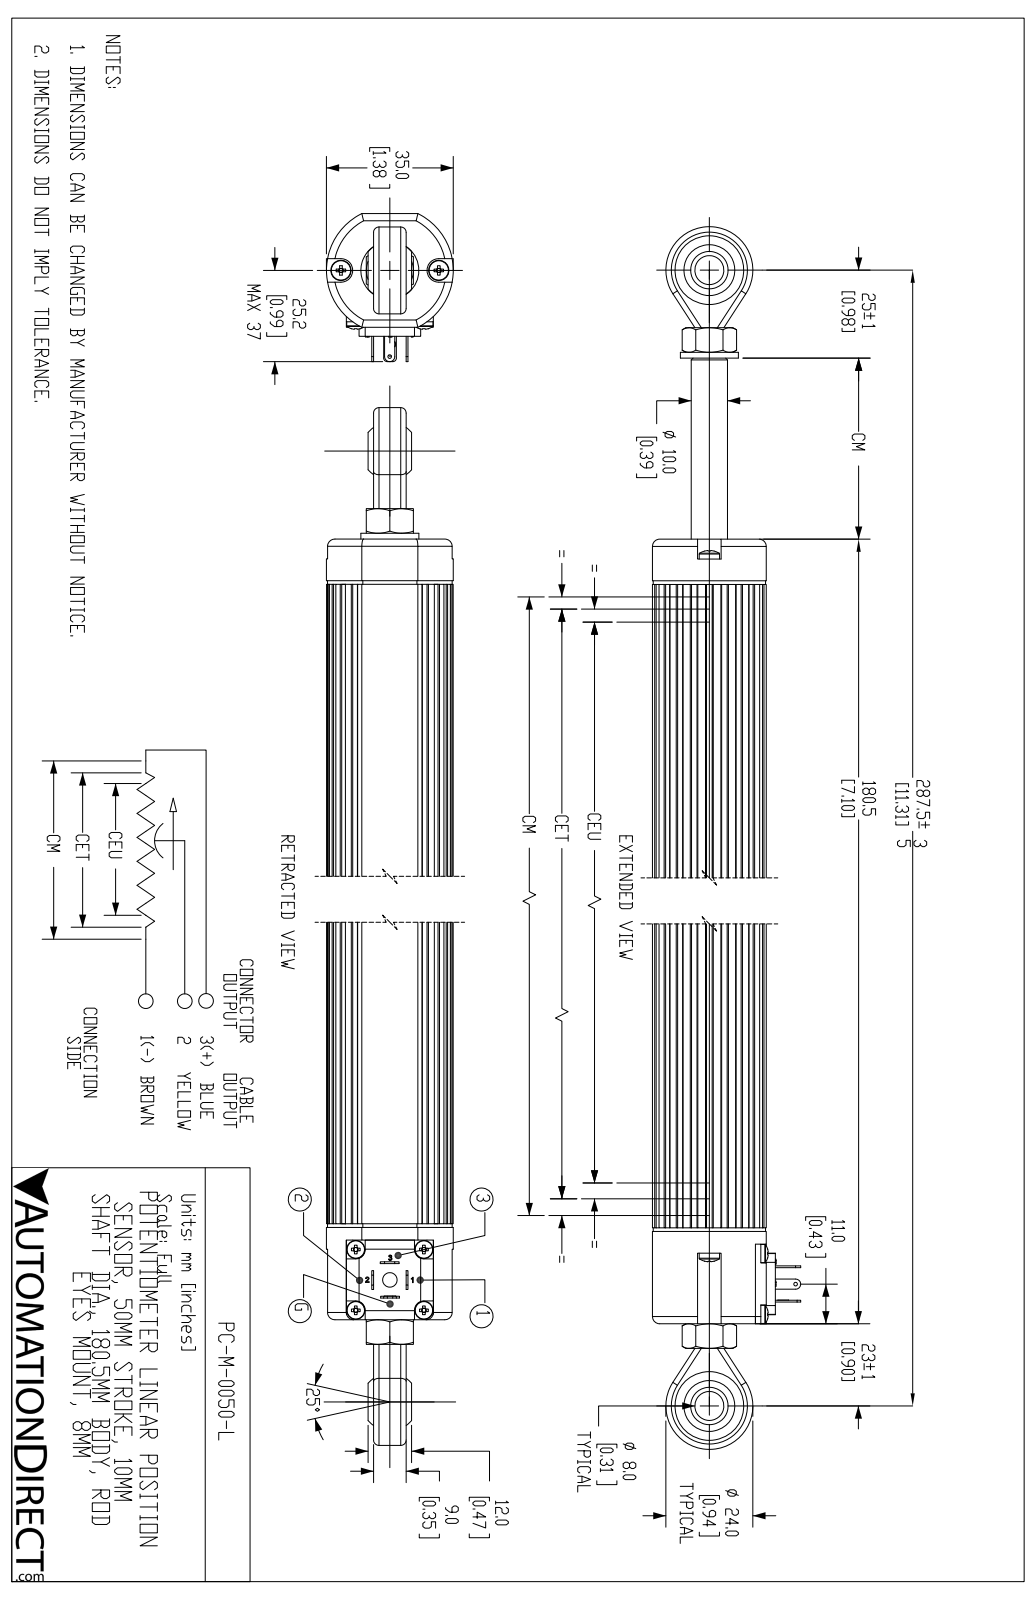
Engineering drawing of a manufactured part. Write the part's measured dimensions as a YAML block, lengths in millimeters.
part_name: "PC-M-0050-L"
step_written_by: "SolidWorks 2019 (AUTOMOTIVE_DESIGN)"
units: millimeters
bodies: {solids: 26, faces: 1441, planar: 437, cylindrical: 366, other: 638}
overall_size: [257.6, 40.9, 35]
volume: 187000
surface_area: 49770
round_holes:
  - {diameter: 2.2, count: 4}
  - {diameter: 2.6, count: 4}
  - {diameter: 1, count: 3}
  - {diameter: 2.7, count: 2}
  - {diameter: 3.5, count: 2}
  - {diameter: 8, count: 2}
  - {diameter: 19, count: 2}
  - {diameter: 2.9, count: 1}
  - {diameter: 4, count: 1}
  - {diameter: 6.8, count: 1}
  - {diameter: 8.4, count: 1}
  - {diameter: 13, count: 1}
round_bosses_or_shafts:
  - {diameter: 5, count: 4}
  - {diameter: 2.5, count: 4}
  - {diameter: 3, count: 3}
  - {diameter: 5.6, count: 2}
  - {diameter: 16, count: 1}
  - {diameter: 10, count: 1}
  - {diameter: 9.9, count: 1}
  - {diameter: 8, count: 1}
partial_cylinders:
  - {radius: 1.5, count: 8}
  - {radius: 1, count: 5}
  - {radius: 2, count: 5}
  - {radius: 2.6, count: 4}
  - {radius: 3, count: 4}
  - {radius: 1.4, count: 2}
  - {radius: 3.3, count: 2}
  - {radius: 12, count: 2}
face_to_face_distances: [1, 31.4, 142.5, 141.5, 143.5, 3, 28.4, 169, 25.5, 26.5]
hole_center_spacings: [12.6, 13.5, 16.8, 18.8, 25.2, 0.6, 2.8, 3.4]
